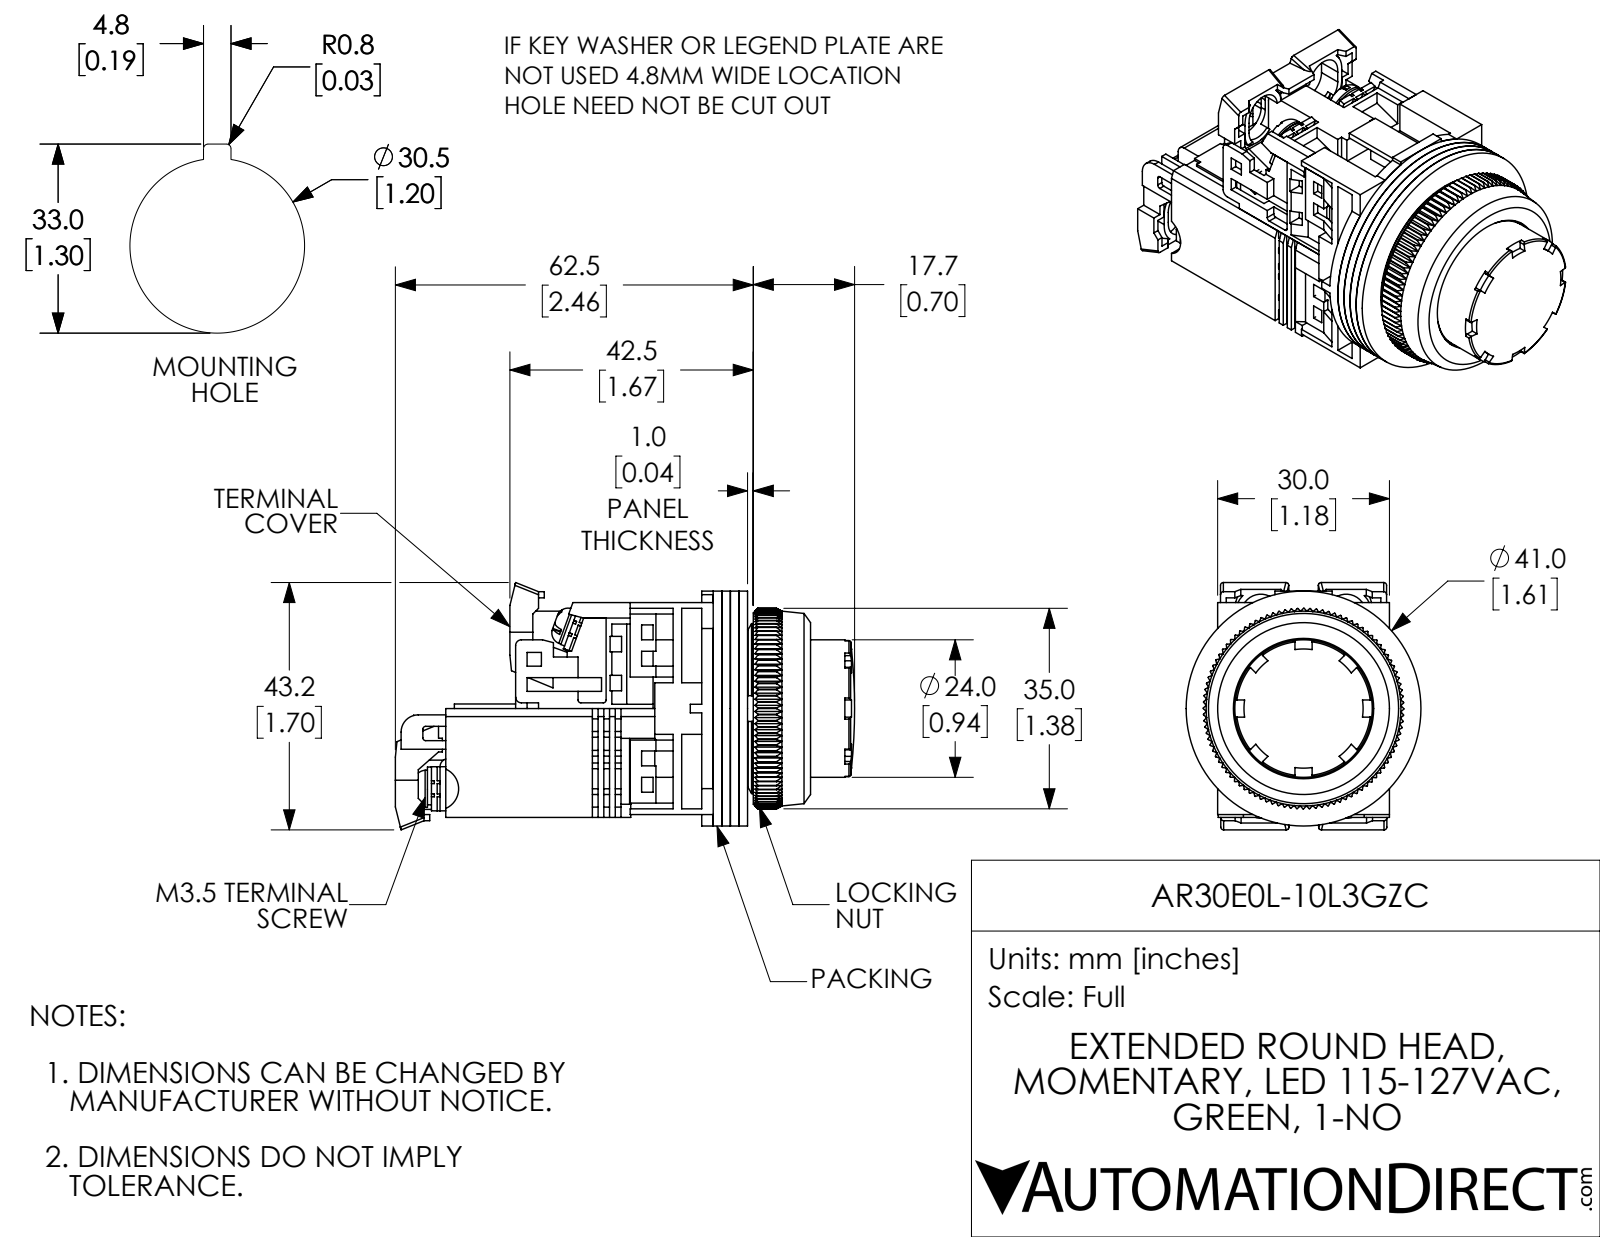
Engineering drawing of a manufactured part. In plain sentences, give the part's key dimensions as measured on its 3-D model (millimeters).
The part is named "AR30E0L-10L3GZC". Its 3-D file was written by "SolidWorks 2017 (AUTOMOTIVE_DESIGN)". It is 27 solids with 1960 faces: 1368 planar, 339 cylindrical and 253 other. Overall it measures 80.2 by 43.2 by 41 millimeters. Its volume is 47 240 cubic millimeters and its surface area 41 310 square millimeters. Round holes: 6 of diameter 3.5, 4 of diameter 3.6, 3 of diameter 3, 1 of diameter 12, 1 of diameter 18, 1 of diameter 18.5, 1 of diameter 20, 1 of diameter 24, 1 of diameter 24.5, 1 of diameter 28.5, 1 of diameter 31.8. Round bosses or shafts: 4 of diameter 6.6, 2 of diameter 3.5, 1 of diameter 41, 1 of diameter 30, 1 of diameter 22, 1 of diameter 19.7, 1 of diameter 14. Partial cylindrical surfaces (rounded edges, fillets, slot ends): 17 of radius 1.5, 16 of radius 0.3, 13 of radius 0.5, 4 of radius 3.5, 4 of radius 4.5, 2 of radius 1, 2 of radius 3, 1 of radius 0.4. The main face-to-face distances are 1.5, 3, 4.5, 19, 1, 0.5, 2, 36, 17.5, 1.2. The hole center spacings are 14.7, 0.5, 7.5, 7.6, 7.6, 14.8, 14.8, 15.4.
